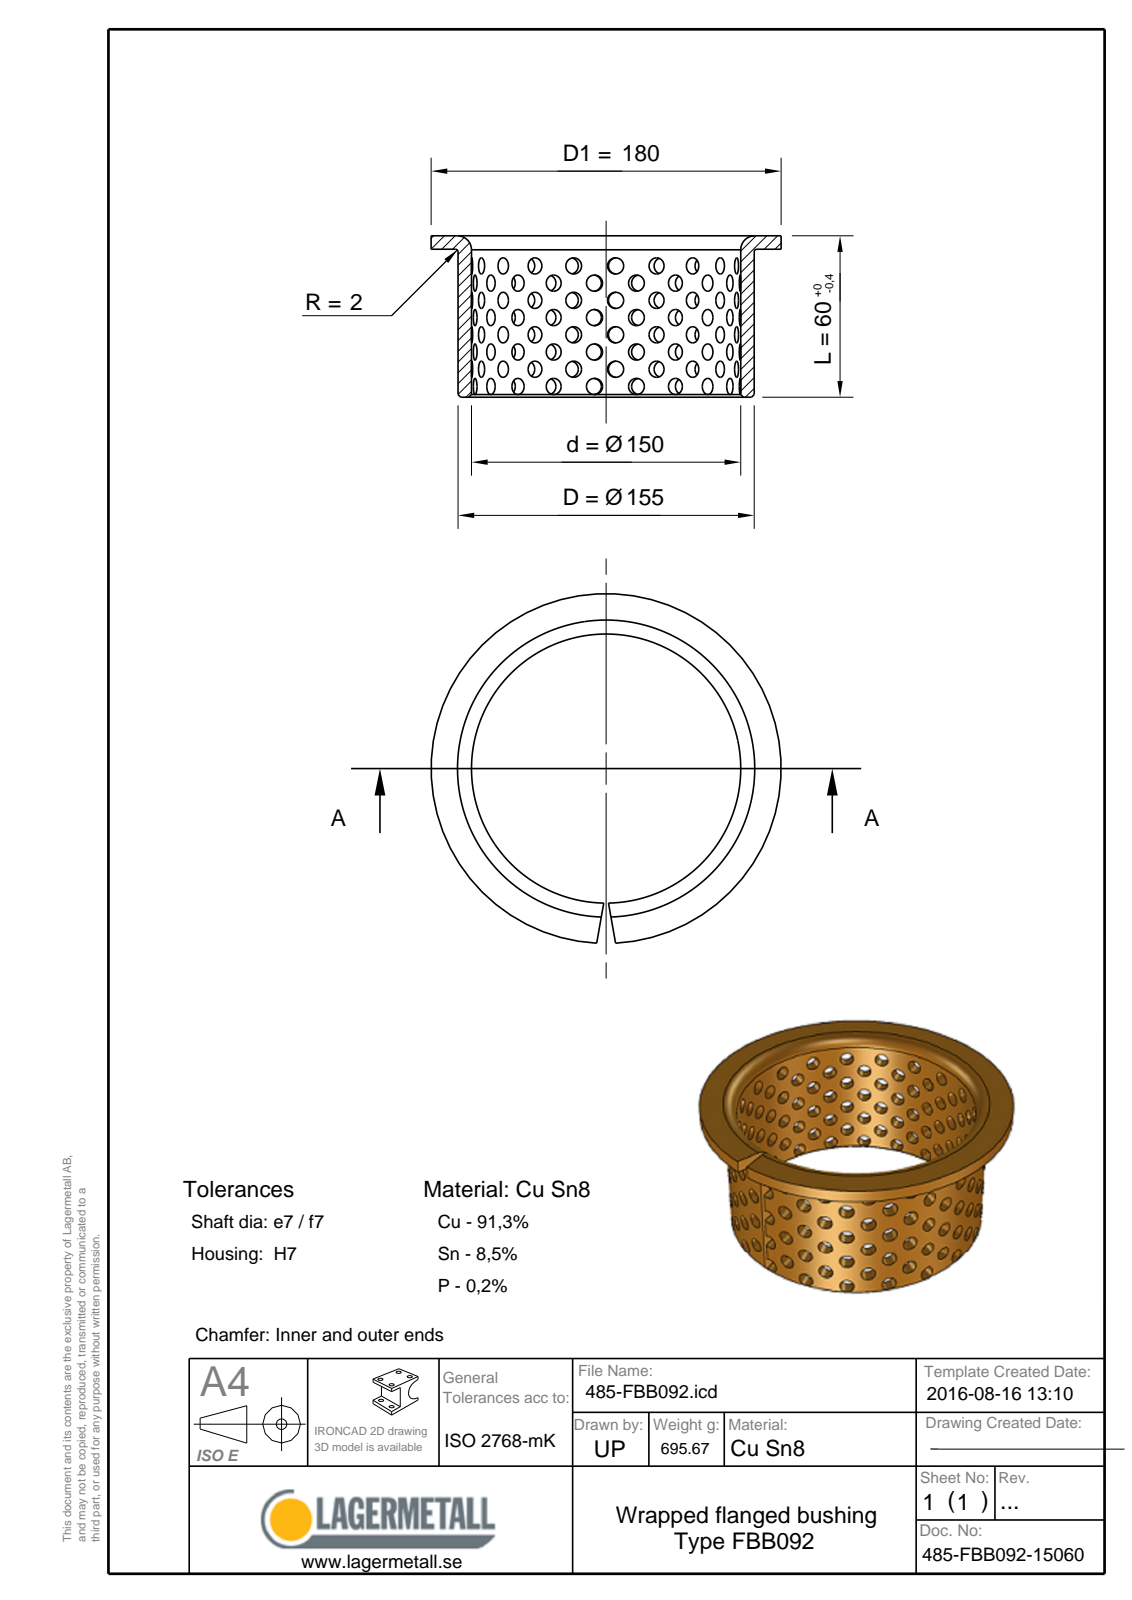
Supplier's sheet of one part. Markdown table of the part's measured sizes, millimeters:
| quantity | value |
| --- | --- |
| part name | 485-FBB092-15060 |
| STEP written by | Spatial InterOp 3D (CONFIG_CONTROL_DESIGN) |
| units | millimeters |
| bodies | 1 solid, 12 faces (5 planar, 3 cylindrical, 4 other) |
| overall size | 180 × 179.95 × 60 |
| volume | 85 885 mm³ |
| surface area | 71 522 mm² |
| round holes (diameter × count) | 150 × 1 |
| round bosses / shafts (diameter × count) | 180 × 1, 155 × 1 |
| main face-to-face distances | 2.5, 57.5, 60 |
